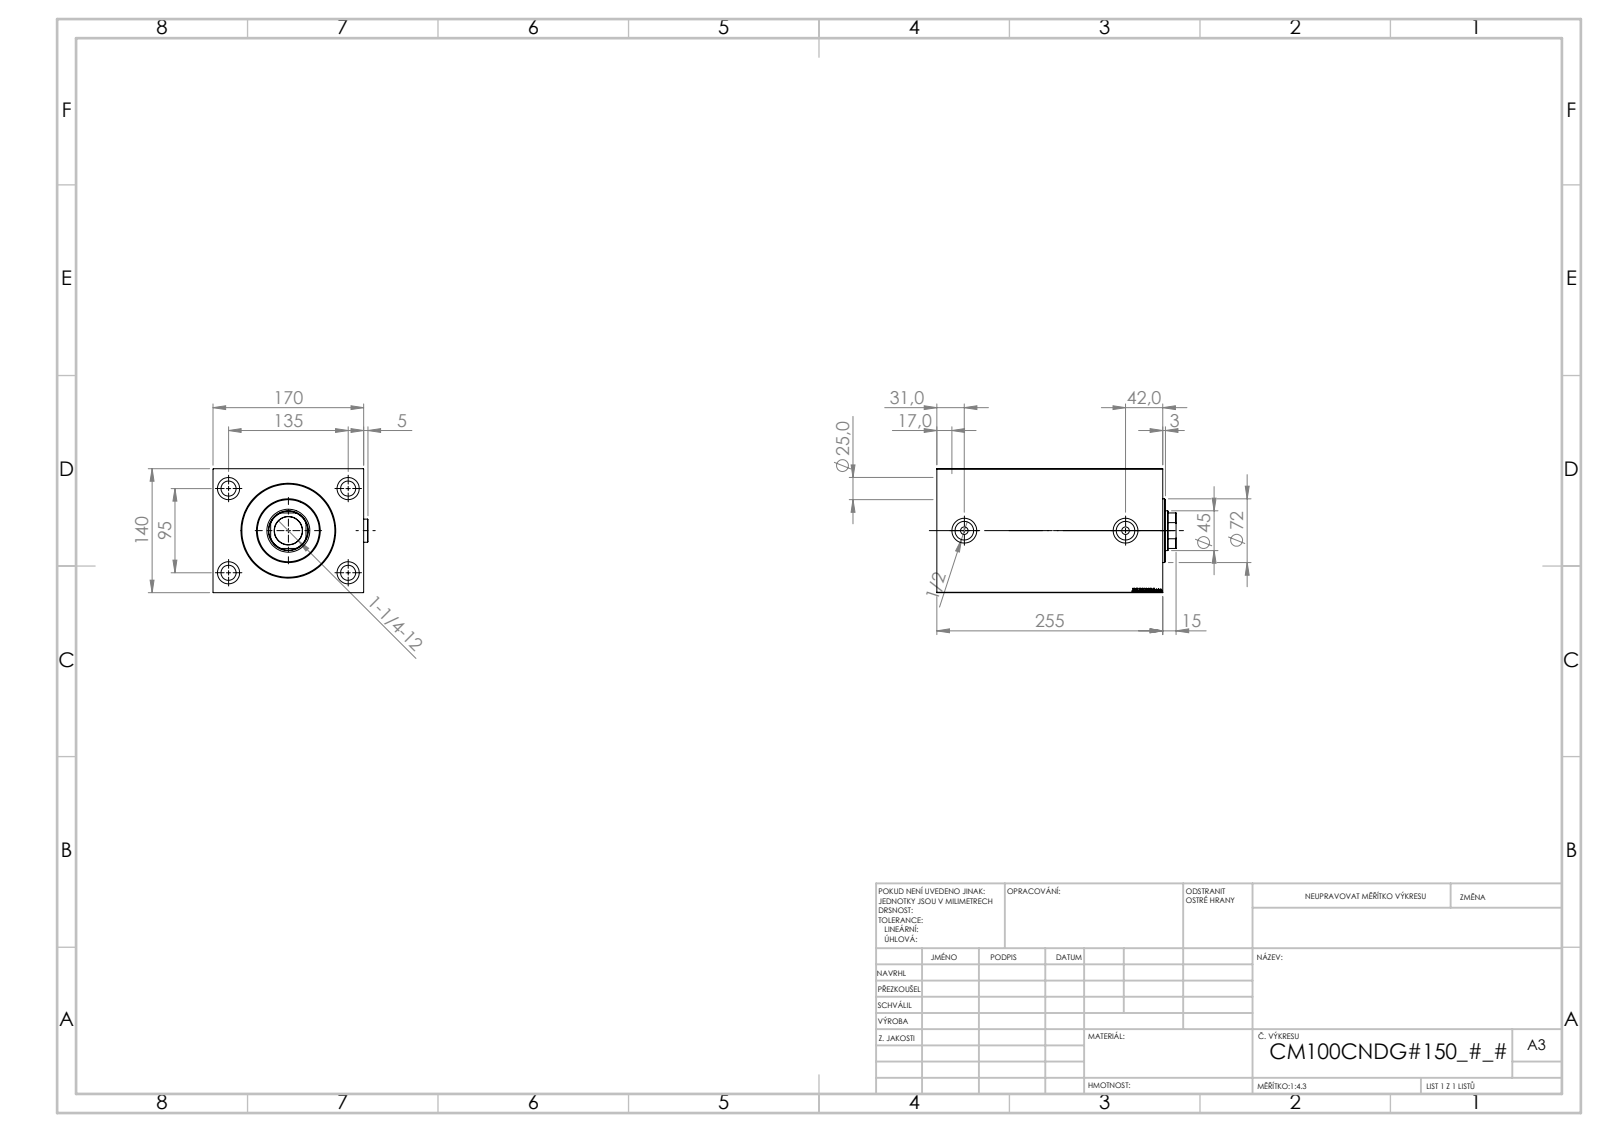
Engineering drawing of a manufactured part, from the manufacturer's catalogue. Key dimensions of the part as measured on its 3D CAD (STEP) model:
Part name (STEP PRODUCT): V450CM_C_VCP; V450CM_C_Body; V450CM_VC_B; Zatka_OIL_PORT
STEP written by: SolidWorks 2019 (CONFIG_CONTROL_DESIGN)
Units: millimetres
Bodies: 5 solids, 919 faces (443 planar, 78 cylindrical, 398 other)
Overall size (bounding box): 270 × 174.9 × 140
Volume: 4 841 000 mm³ · Surface area: 429 063 mm²
Round holes (diameter × count): ⌀17 ×4, ⌀25 ×4, ⌀8.5 ×2, ⌀20.96 ×2, ⌀28 ×2, ⌀31.5 ×1, ⌀45 ×1, ⌀48.5 ×1, ⌀100 ×1, ⌀102 ×1, ⌀105 ×1
Round bosses / shafts (diameter × count): ⌀26 ×2, ⌀72 ×1
Partial cylindrical surfaces — rounded edges, fillets, slot ends (radius × count): R22 ×1
Main face-to-face distances: 140, 170, 255, 229, 26, 15, 214, 240, 90, 165
Hole centre spacings: 82.54, 95, 135, 165.08, 182
